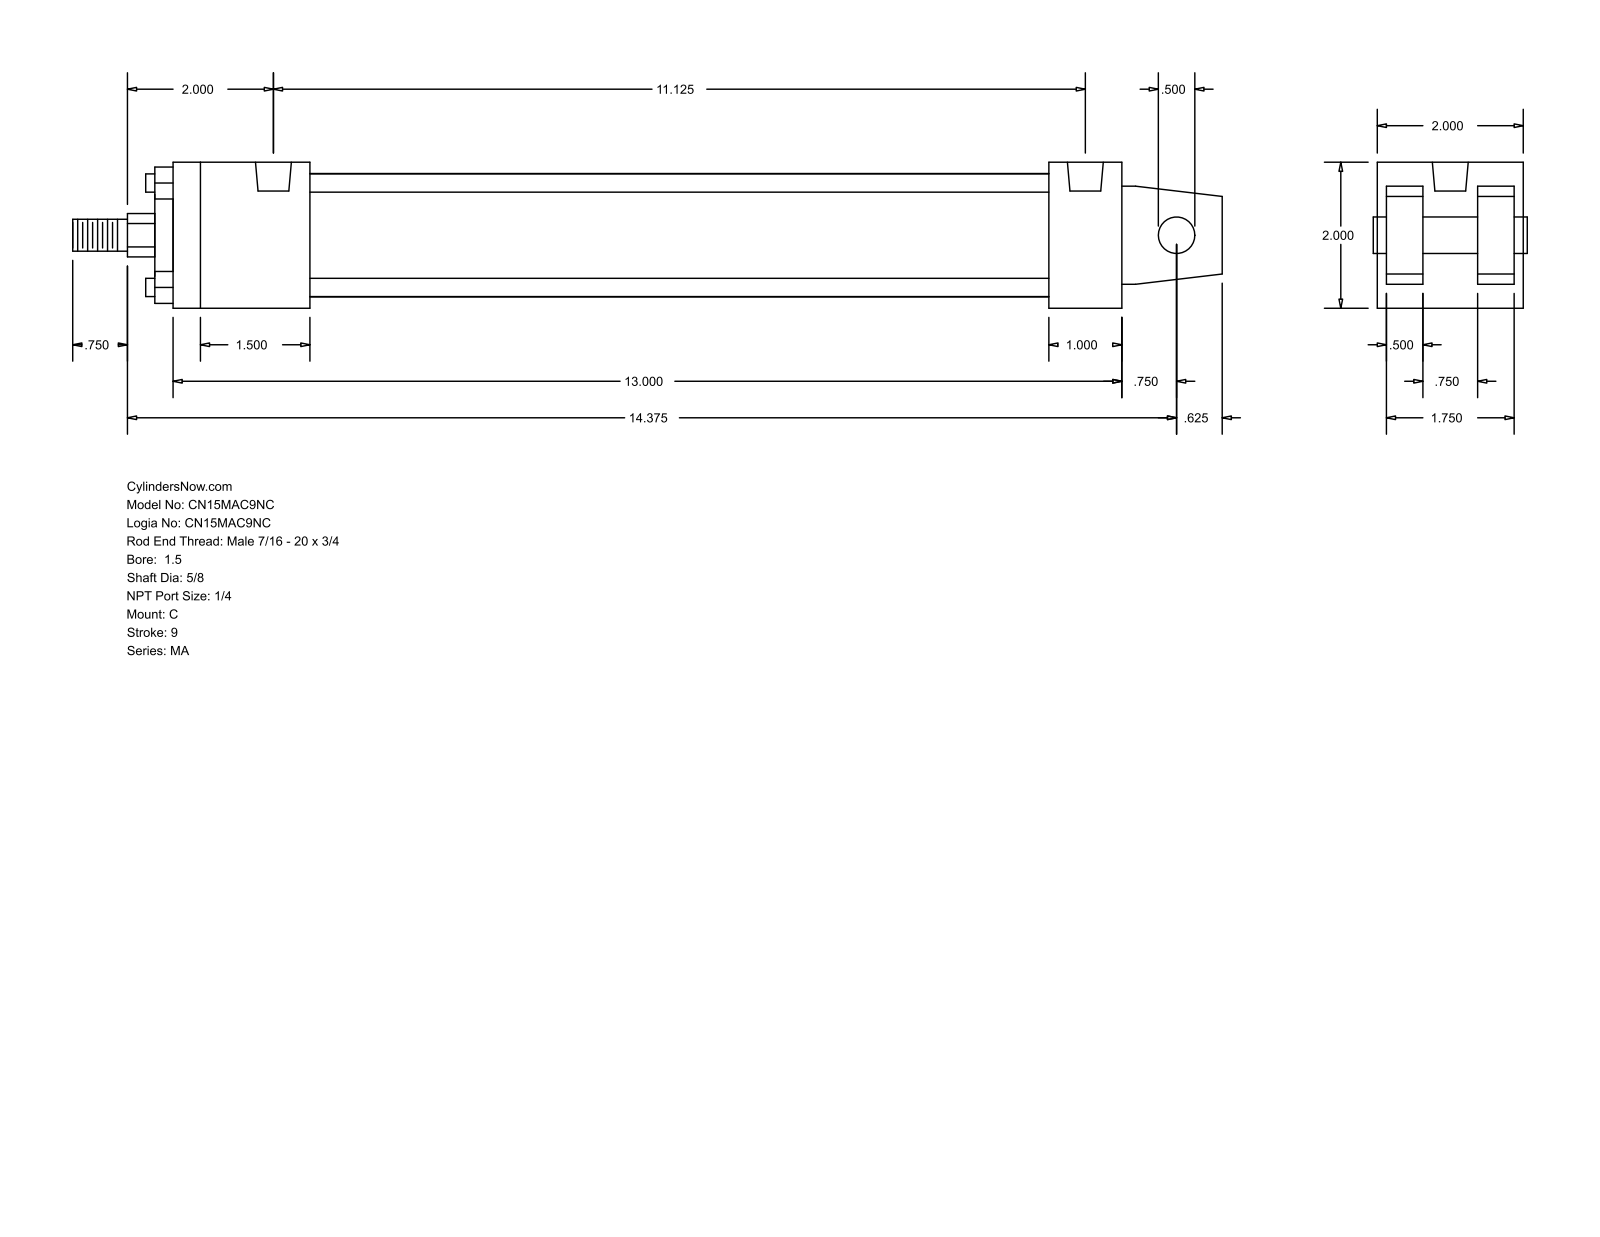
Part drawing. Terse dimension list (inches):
name: MA_C__0150_0.625
written by: GSSL Pune (CONFIG_CONTROL_DESIGN)
unit: in
bodies: 0 solids, 103 faces (76 planar, 27 cylindrical, 0 other)
size: 15.75 × 2 × 2
holes: 4× ⌀0.313, 2× ⌀0.492
bosses: 4× ⌀0.25, 1× ⌀1.69, 1× ⌀1.125, 1× ⌀0.625, 1× ⌀0.5, 1× ⌀0.437
rounds: 1× R0.297
face distances: 2, 1.375, 0.5, 0.625, 0.125, 1.875, 1.25, 13, 12, 1
hole spacings: 11.125
